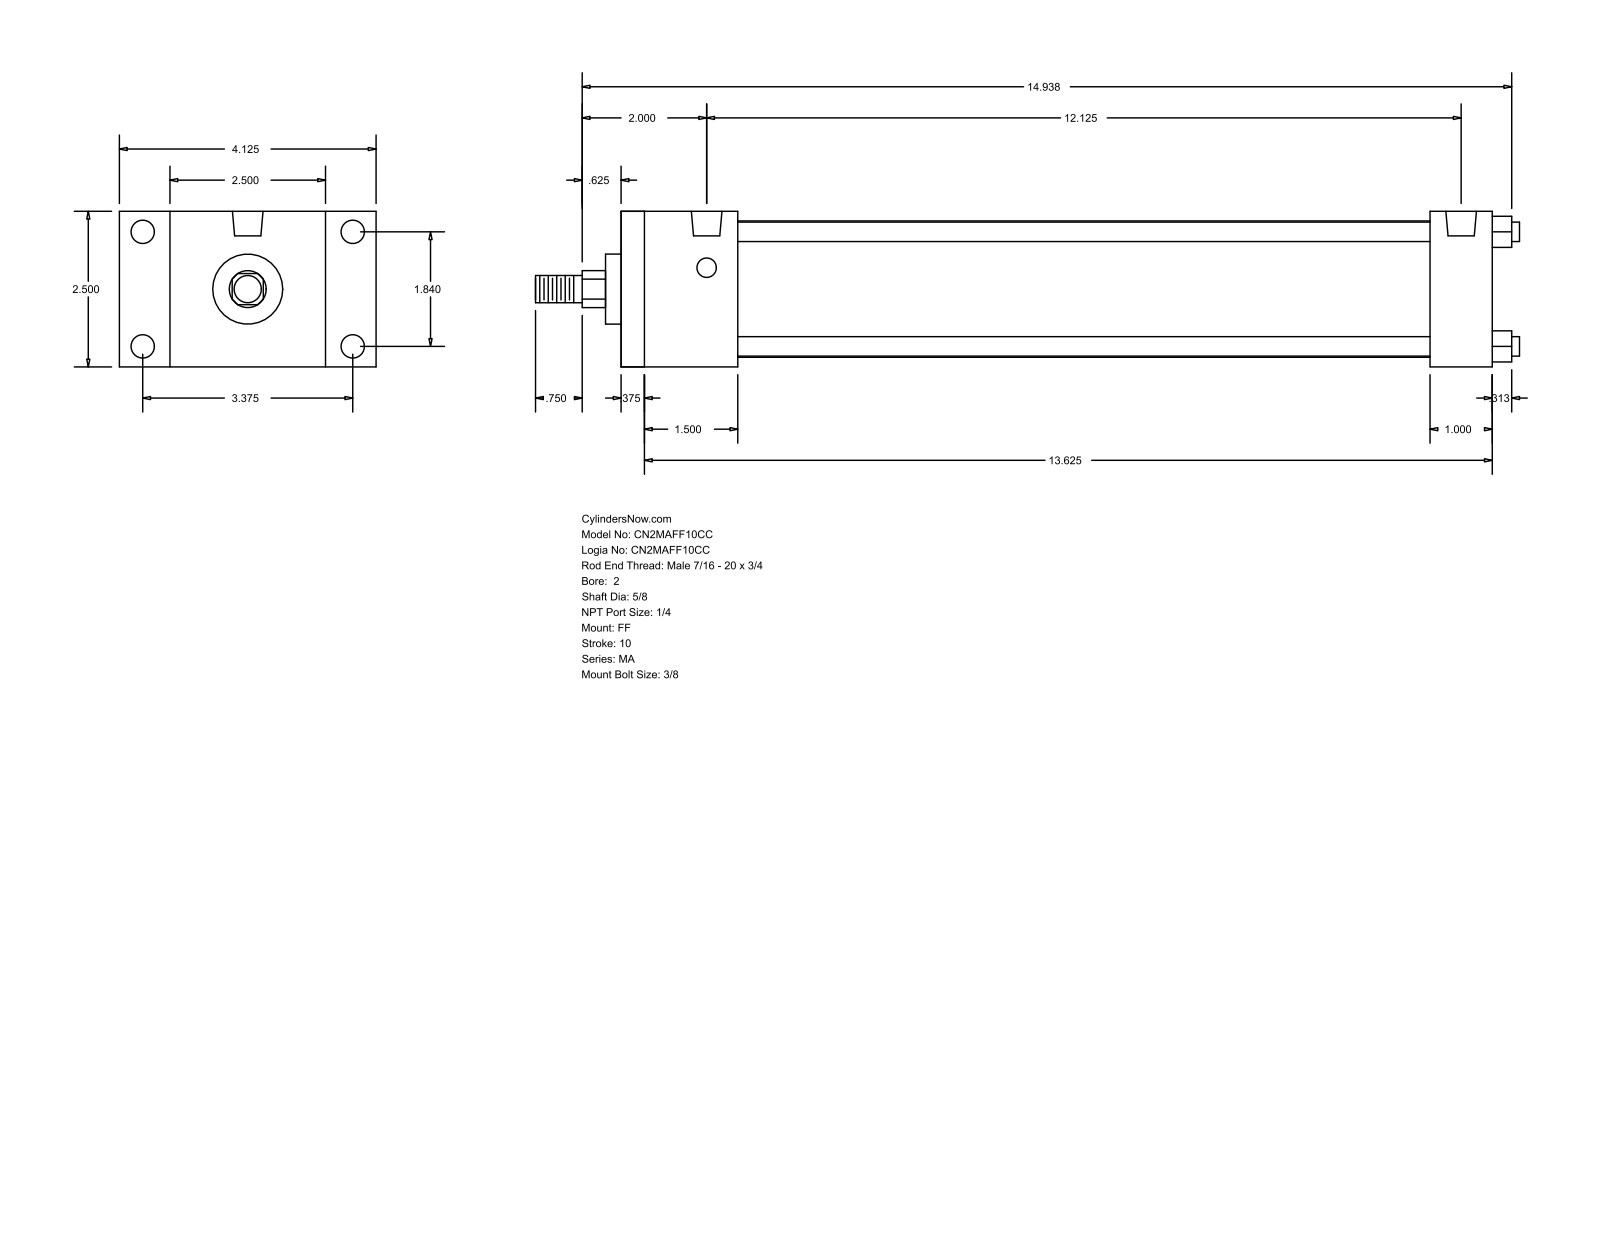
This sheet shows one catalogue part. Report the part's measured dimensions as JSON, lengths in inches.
{"part_name": "MA_FF__0200_0.625", "step_written_by": "GSSL Pune (CONFIG_CONTROL_DESIGN)", "units": "inches", "bodies": {"solids": 0, "faces": 92, "planar": 64, "cylindrical": 28, "other": 0}, "overall_size": [15.813, 4.125, 2.5], "round_holes": [[0.313, 4], [0.375, 4], [0.492, 2]], "round_bosses_or_shafts": [[0.313, 4], [2.19, 1], [1.125, 1], [0.625, 1], [0.437, 1]], "partial_cylinders_radius": [[0.297, 1]], "face_to_face_distances": [2.5, 14, 0.375, 13.625, 1.5, 1.875, 13, 12.625, 11.125, 12.125], "hole_center_spacings": [1.84, 3.375, 3.844, 12.125]}
